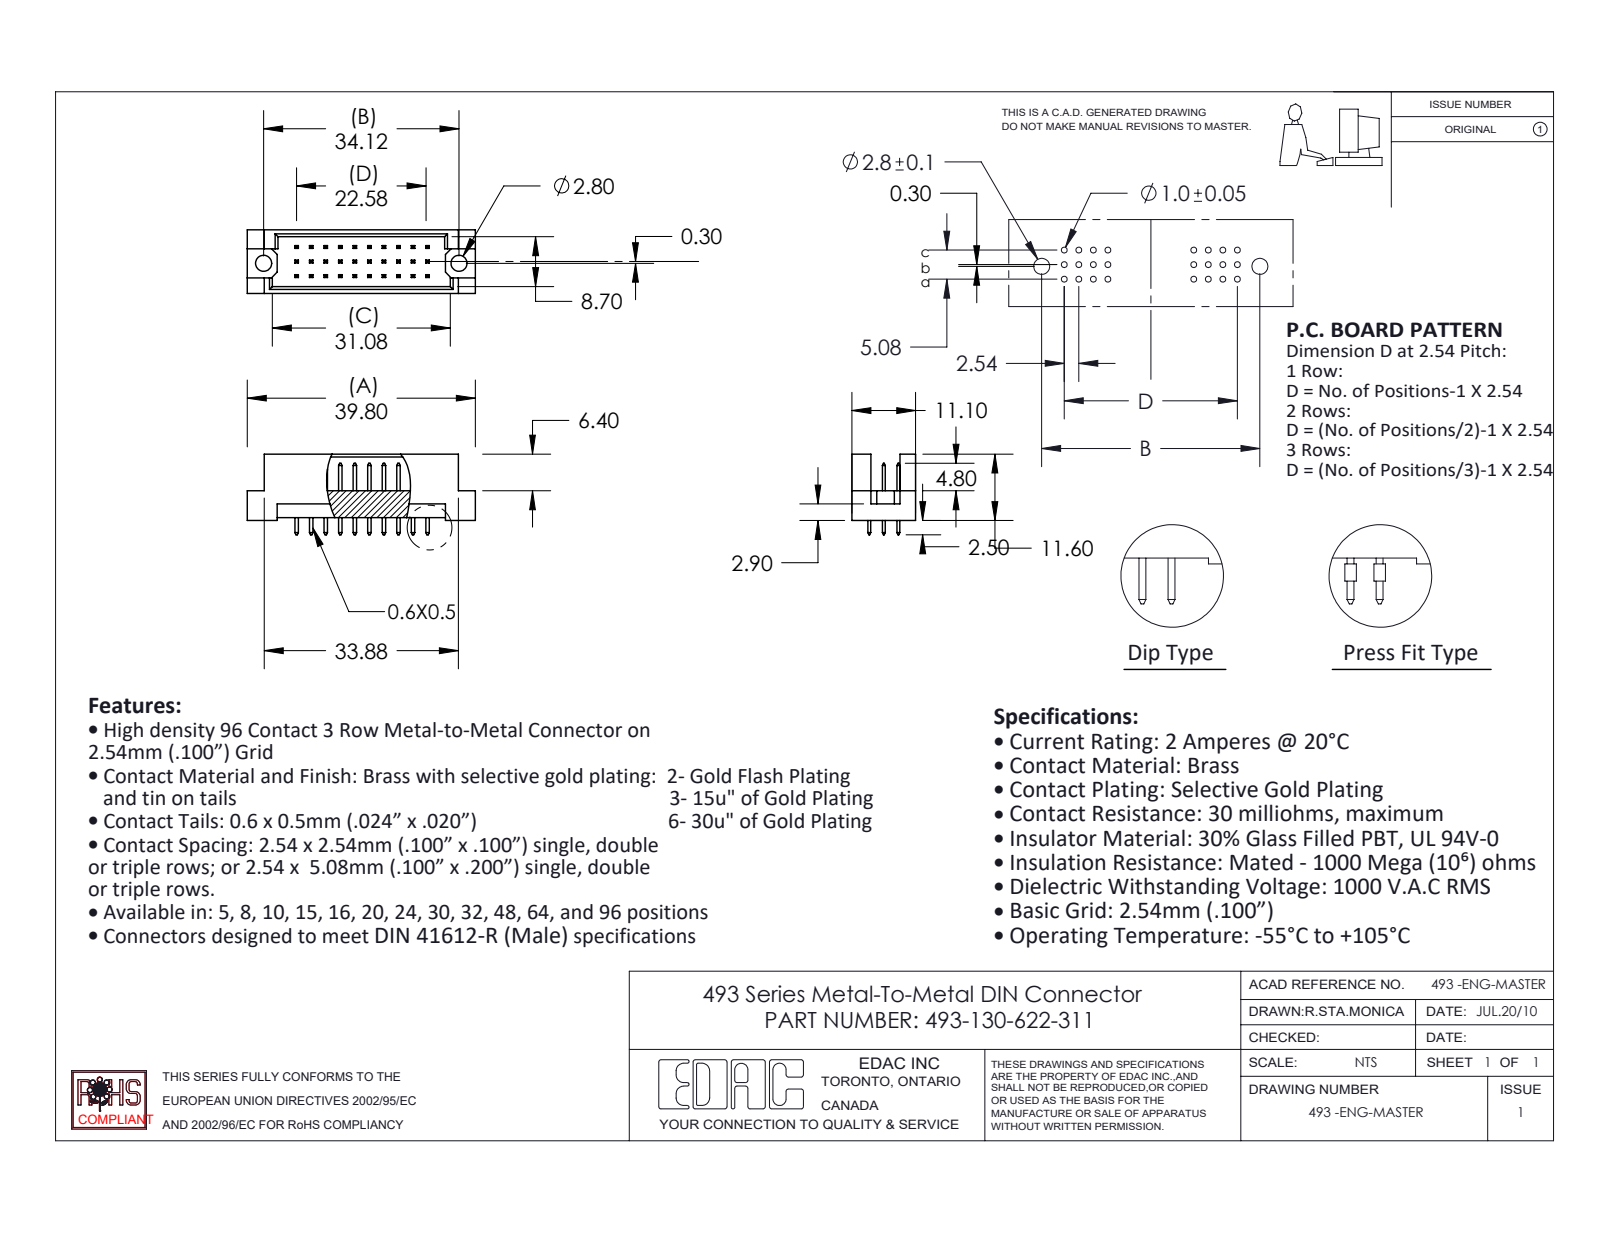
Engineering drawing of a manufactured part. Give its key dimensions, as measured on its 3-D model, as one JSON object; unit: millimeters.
{"part_name": "493 Part_30; 493-130-622-311; 493-290_22", "step_written_by": "SolidWorks 2020 (CONFIG_CONTROL_DESIGN)", "units": "millimeters", "bodies": {"solids": 31, "faces": 592, "planar": 588, "cylindrical": 4, "other": 0}, "overall_size": [39.8, 14.1, 11.1], "volume_mm3": 2482, "surface_area_mm2": 3551, "round_holes": [[2.8, 2]], "face_to_face_distances": [2.54, 5.08, 1.2, 9.9, 11.1, 0.5, 8.7, 4.7, 7.62, 10.16], "hole_center_spacings": [34.12]}
